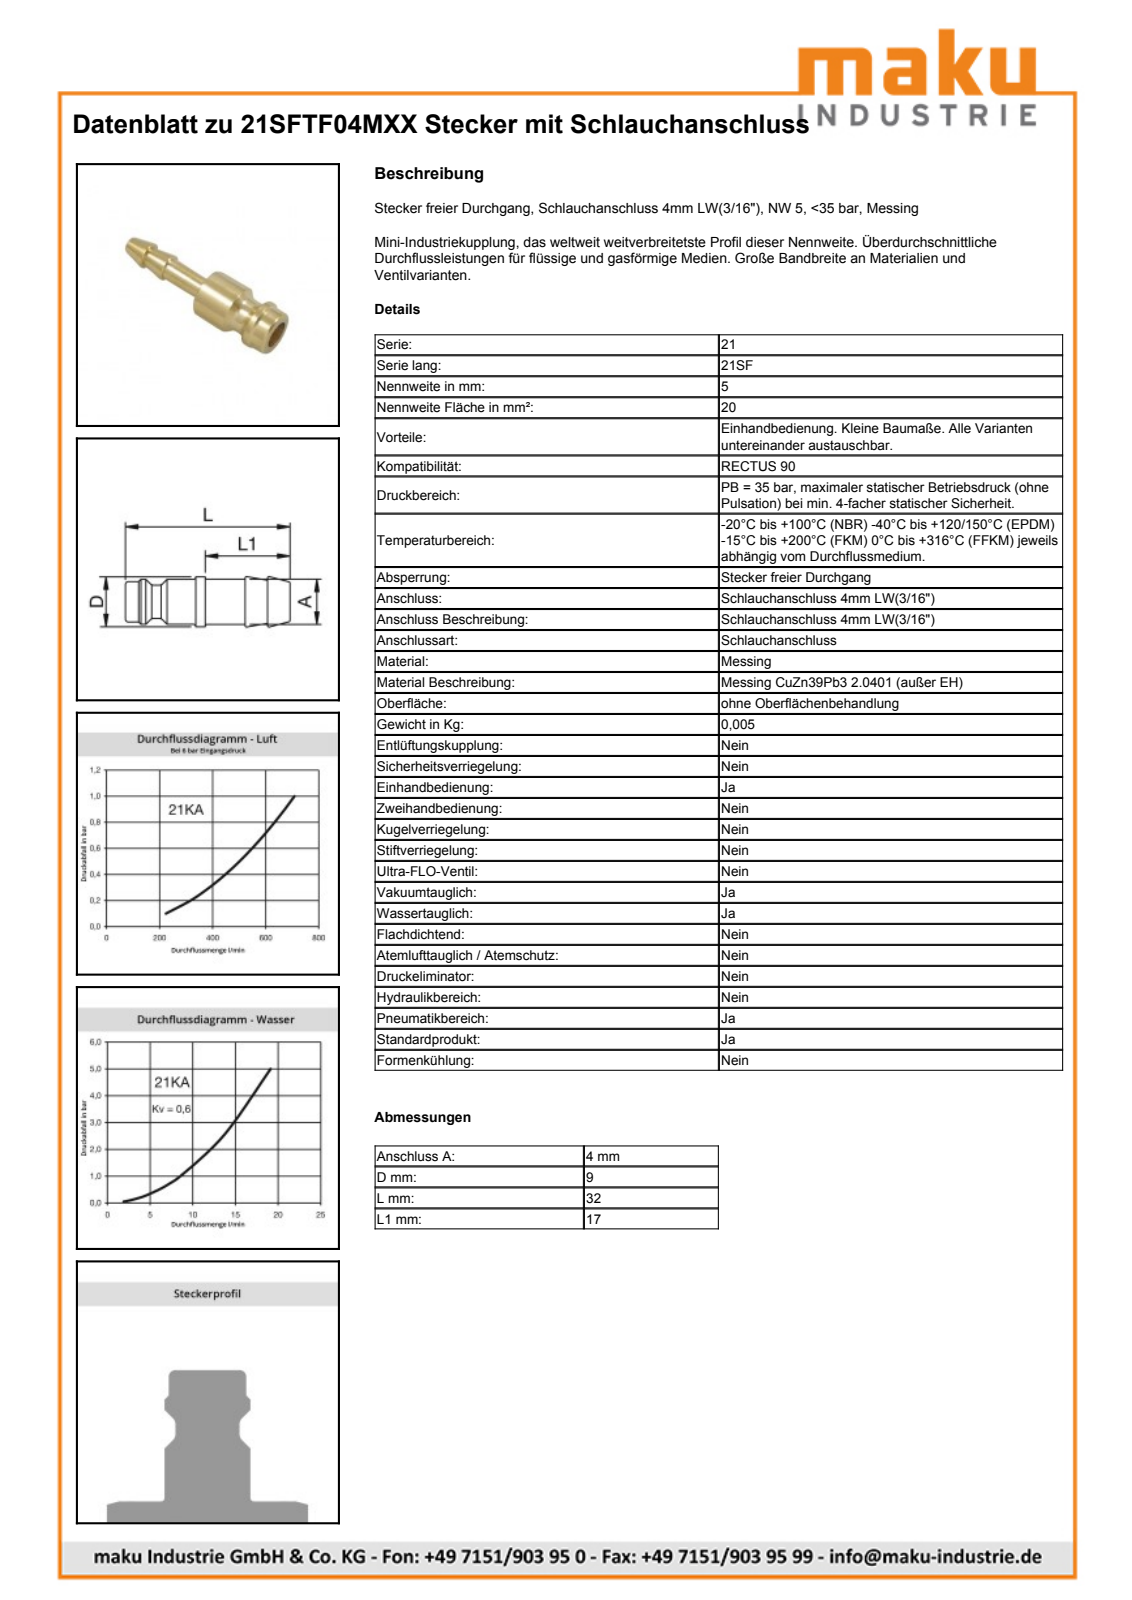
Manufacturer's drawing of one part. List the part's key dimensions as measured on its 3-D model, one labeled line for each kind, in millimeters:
Part name (STEP PRODUCT): D109242
STEP written by: Autodesk Inventor 2013 (AUTOMOTIVE_DESIGN)
Units: millimetres
Bodies: 1 solid, 26 faces (5 planar, 7 cylindrical, 14 other)
Overall size (bounding box): 32 × 9 × 9
Volume: 712 mm³ · Surface area: 1 091 mm²
Round holes (diameter × count): ⌀2.5 ×1, ⌀4.95 ×1
Round bosses / shafts (diameter × count): ⌀9 ×1, ⌀8.1 ×1, ⌀6.65 ×1, ⌀4.05 ×1
Main face-to-face distances: 15, 12.5, 27.5, 4.5, 8, 23, 9, 17, 32
